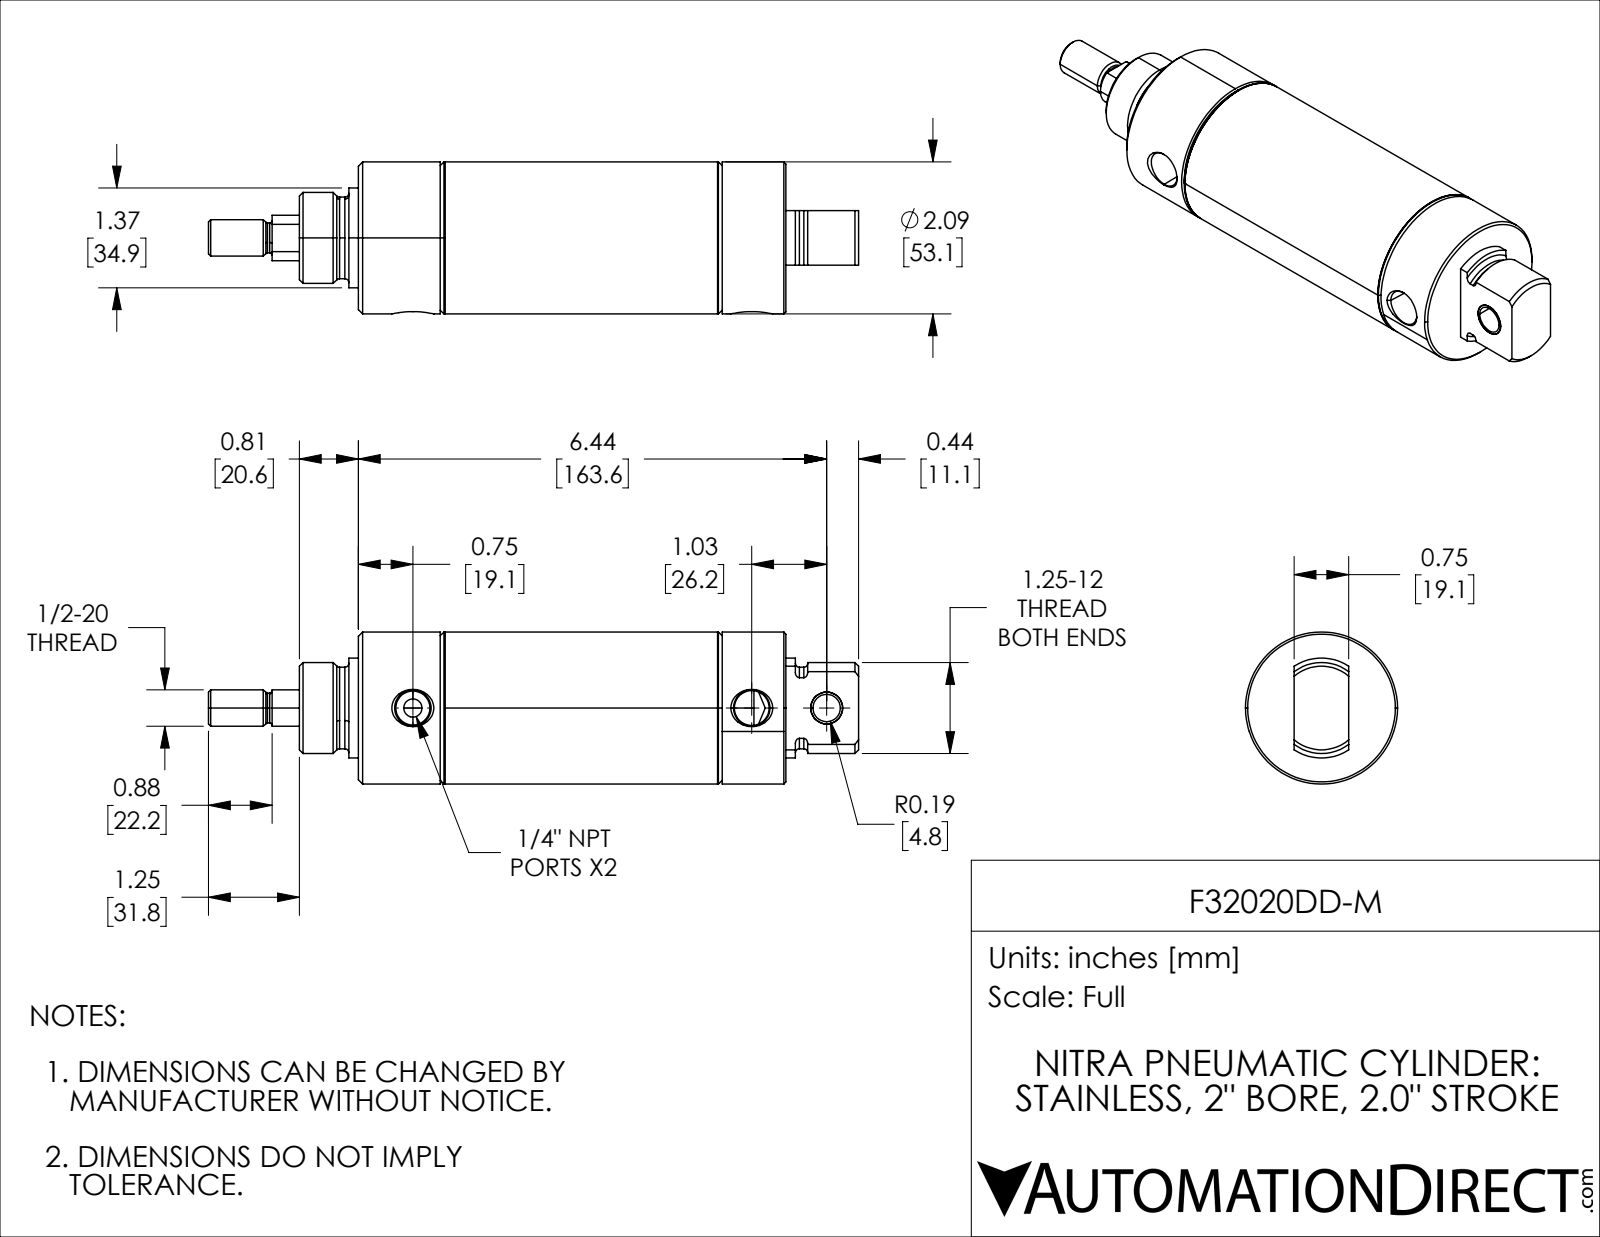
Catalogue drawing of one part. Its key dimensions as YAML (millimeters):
part_name: "F32020DD-M_3; F32020DD-M_9; F32020DD-M_5; F32020DD-M (+2 more)"
step_written_by: "SolidWorks 2021 (CONFIG_CONTROL_DESIGN)"
units: millimeters
bodies: {solids: 5, faces: 160, planar: 31, cylindrical: 60, other: 69}
overall_size: [227.03, 53.09, 53.09]
volume: 253845
surface_area: 81222
round_holes:
  - {diameter: 6.35, count: 1}
  - {diameter: 9.55, count: 1}
  - {diameter: 11.15, count: 1}
  - {diameter: 12.18, count: 1}
  - {diameter: 16.52, count: 1}
  - {diameter: 19.05, count: 1}
  - {diameter: 49.05, count: 1}
round_bosses_or_shafts:
  - {diameter: 53.09, count: 1}
  - {diameter: 51.16, count: 1}
  - {diameter: 34.87, count: 1}
  - {diameter: 31.75, count: 1}
  - {diameter: 28.51, count: 1}
  - {diameter: 15.88, count: 1}
  - {diameter: 12.7, count: 1}
  - {diameter: 10.46, count: 1}
partial_cylinders:
  - {radius: 14.25, count: 1}
face_to_face_distances: [30.17, 50.8, 80.97, 111.2, 60.4, 30.23, 38.15, 88.95, 119.12, 149.35]
hole_center_spacings: [26.16, 118.36, 144.52]
